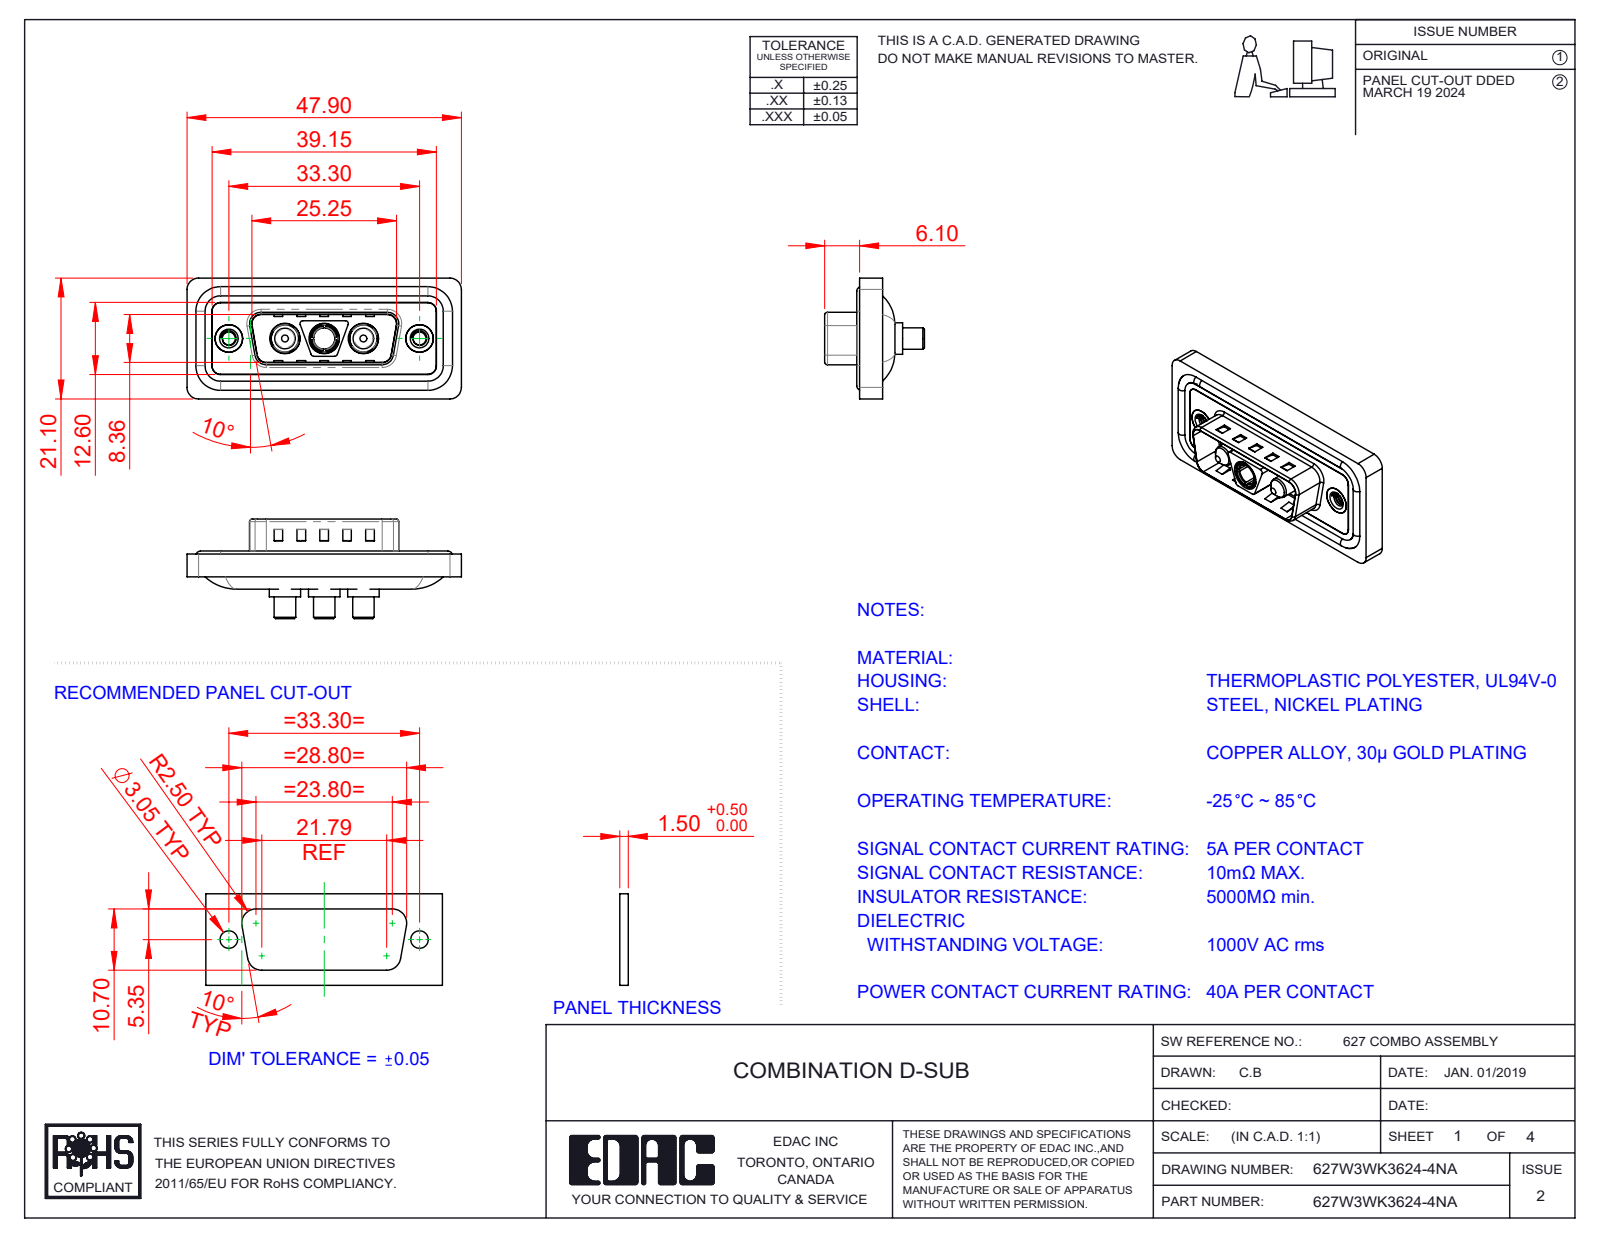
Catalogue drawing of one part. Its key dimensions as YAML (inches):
part_name: "627Combo Housing_3WK3; 627Combo Threaded Rivet_A; 627Combo Shell Rear_15 Contacts; 627Combo Shell Front_15 Contacts (+4 more)"
step_written_by: "SolidWorks 2023 (CONFIG_CONTROL_DESIGN)"
units: inches
bodies: {solids: 13, faces: 607, planar: 231, cylindrical: 252, other: 124}
overall_size: [1.886, 0.831, 0.685]
volume: 0.351
surface_area: 14.19
round_holes:
  - {diameter: 0.191, count: 3}
  - {diameter: 0.209, count: 3}
  - {diameter: 0.089, count: 2}
  - {diameter: 0.157, count: 2}
  - {diameter: 0.189, count: 2}
  - {diameter: 0.197, count: 2}
  - {diameter: 0.146, count: 1}
round_bosses_or_shafts:
  - {diameter: 0.063, count: 4}
  - {diameter: 0.217, count: 3}
  - {diameter: 0.205, count: 3}
  - {diameter: 0.187, count: 3}
  - {diameter: 0.148, count: 3}
  - {diameter: 0.193, count: 2}
  - {diameter: 0.142, count: 2}
  - {diameter: 0.195, count: 1}
partial_cylinders:
  - {radius: 0.059, count: 26}
  - {radius: 0.079, count: 20}
  - {radius: 0.02, count: 12}
  - {radius: 0.063, count: 8}
  - {radius: 0.01, count: 4}
  - {radius: 0.024, count: 4}
  - {radius: 0.026, count: 4}
  - {radius: 0.035, count: 4}
face_to_face_distances: [0.016, 0.043, 0.02, 0.059, 0.063, 0.122, 0.114, 0.157, 0.032, 0.377]
hole_center_spacings: [0.27, 0.386, 0.656, 0.925, 0.539, 1.311]
